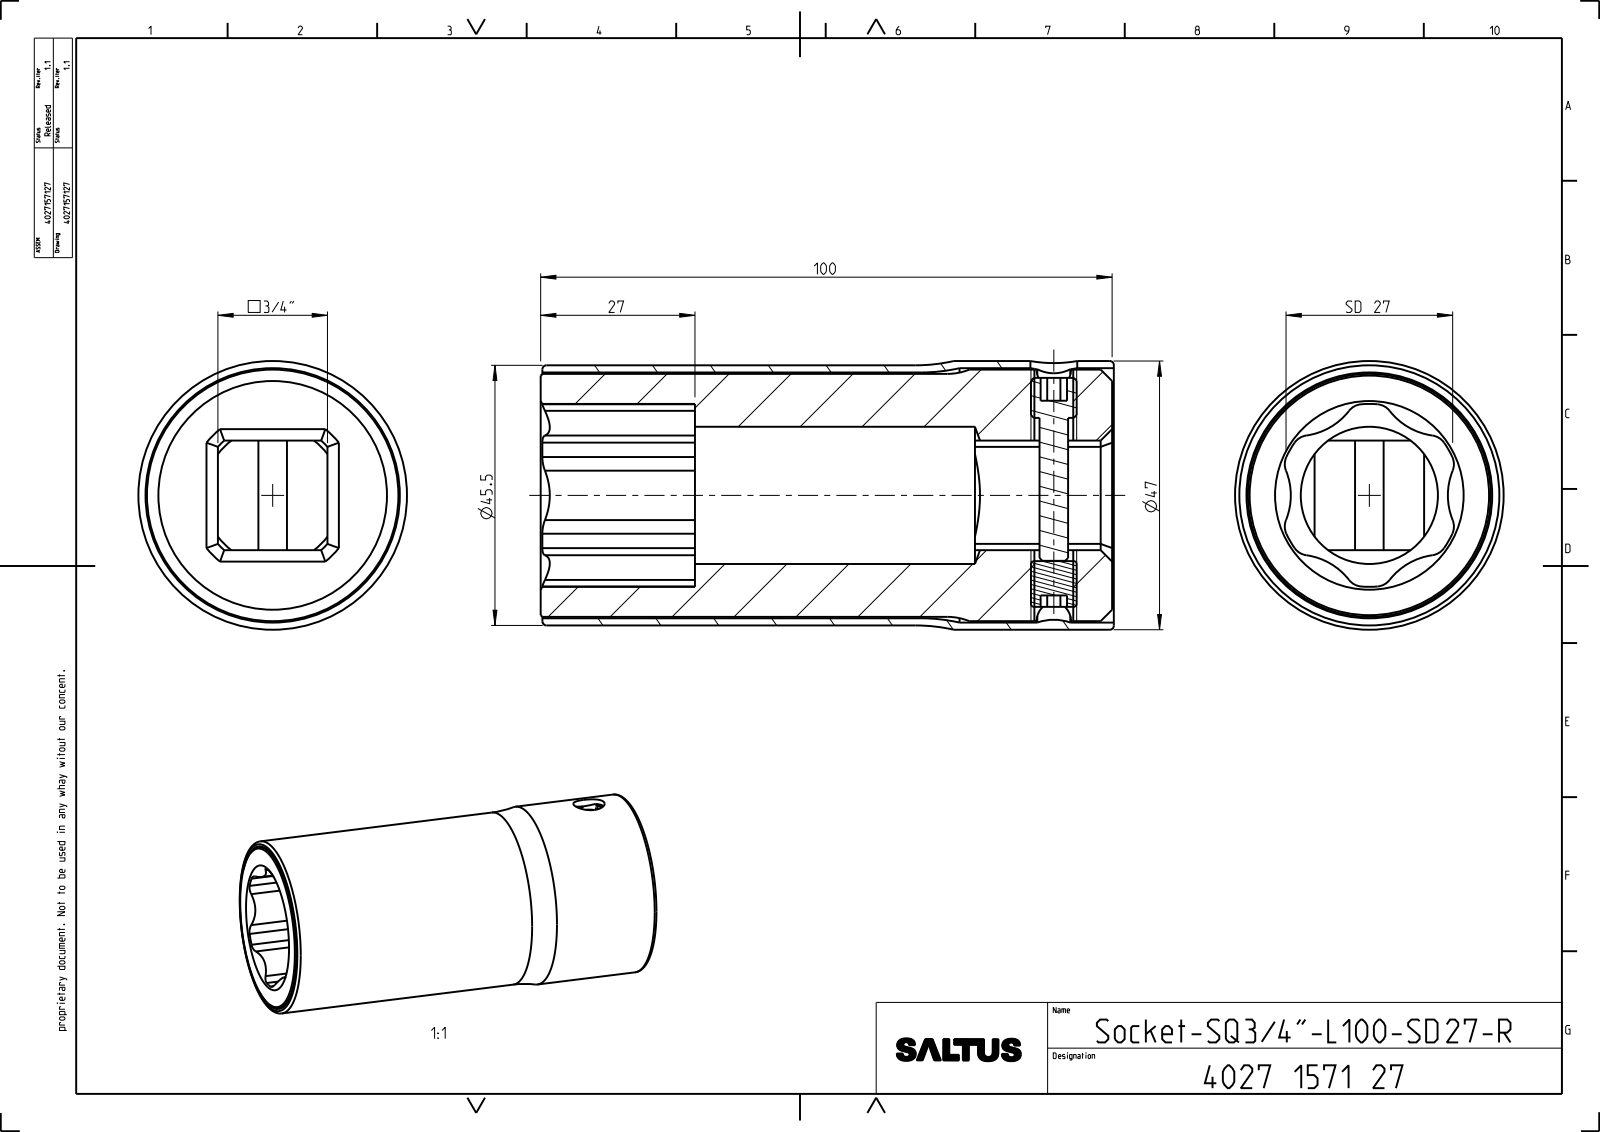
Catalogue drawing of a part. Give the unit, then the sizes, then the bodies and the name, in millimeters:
Units: millimetres
Overall size (bounding box): 100.3 × 47 × 47
Round holes (diameter × count): ⌀6.8 ×1, ⌀8 ×1, ⌀8.2 ×1, ⌀24 ×1, ⌀43 ×1, ⌀44.5 ×1
Round bosses / shafts (diameter × count): ⌀47 ×1, ⌀45.5 ×1, ⌀44 ×1, ⌀42.5 ×1, ⌀5 ×1
Partial cylindrical surfaces — rounded edges, fillets, slot ends (radius × count): R3 ×12, R11.5 ×6, R12.8 ×1, R16 ×1
Main face-to-face distances: 19.18, 100, 73, 27, 73.3, 100.3, 99.7, 26.7, 4, 1.91
Volume: 110 458 mm³ · Surface area: 54 046 mm²
Bodies: 4 solids, 135 faces (36 planar, 62 cylindrical, 37 other)
Part name (STEP PRODUCT): 4027911336; 4027044175; 0190131800_SPEC; 4027905697 (+1 more)
STEP written by: CREO PARAMETRIC BY PTC INC, 2022414 (CONFIG_CONTROL_DESIGN)
